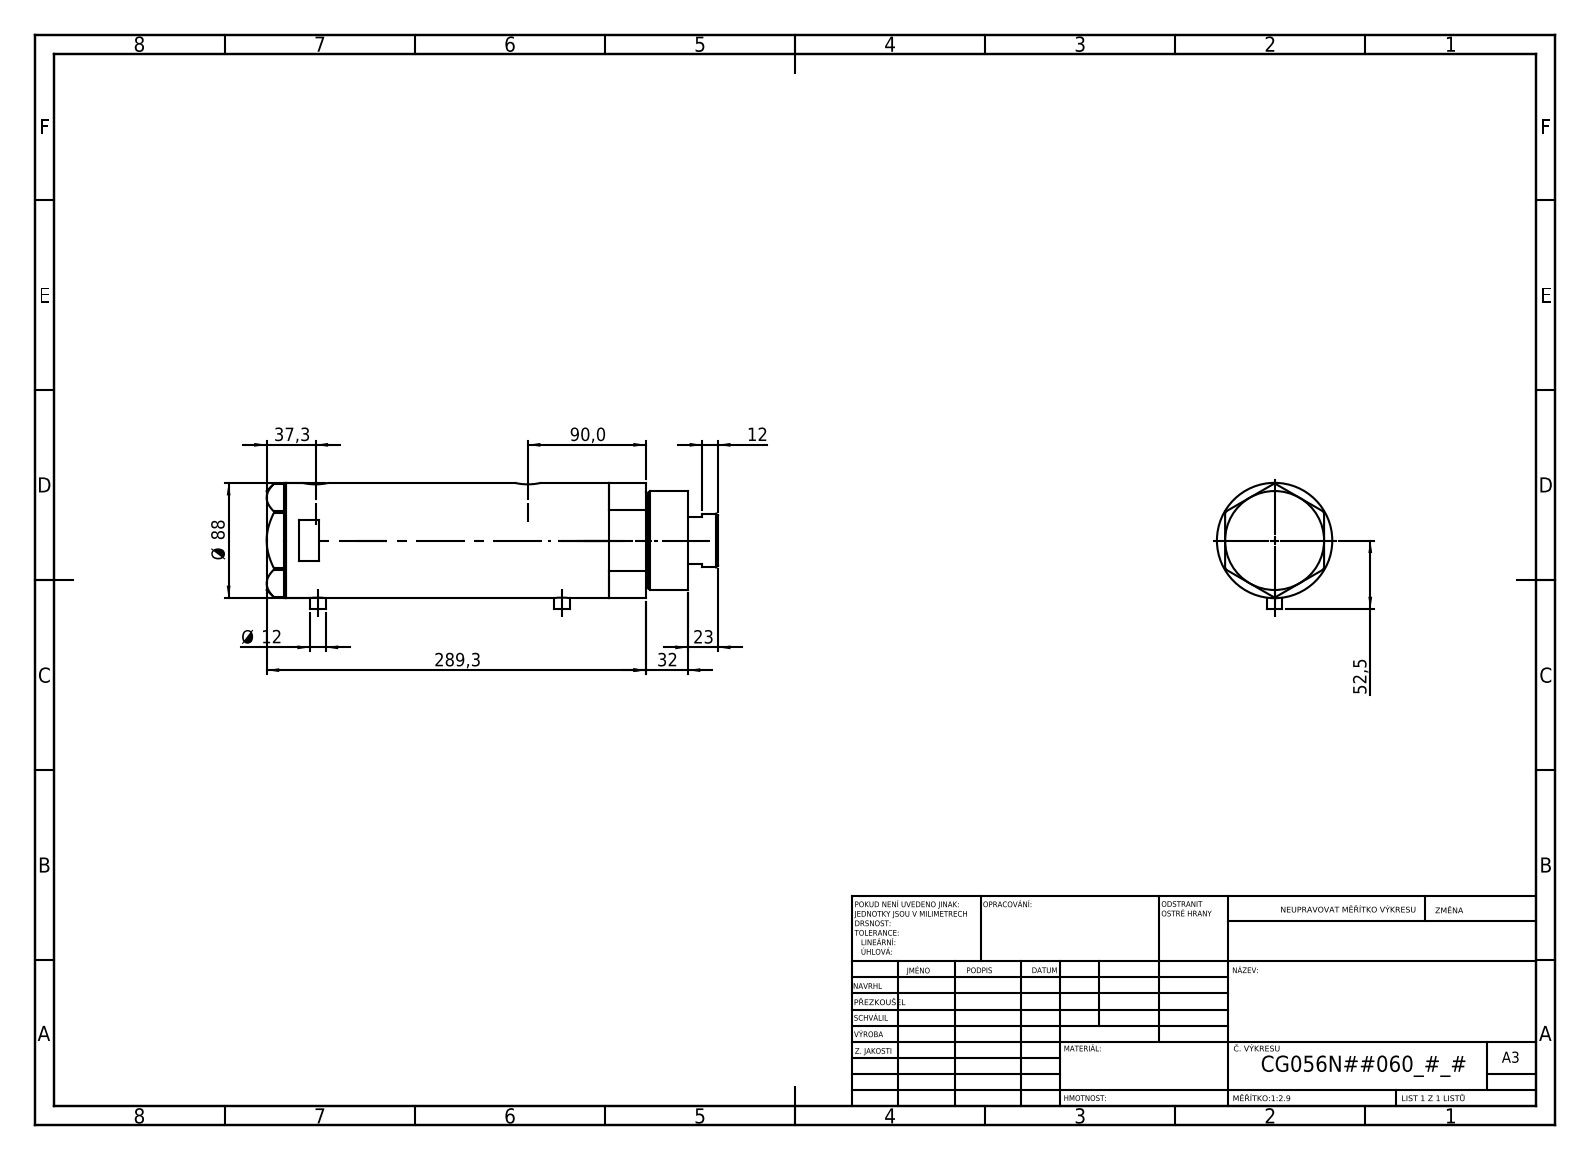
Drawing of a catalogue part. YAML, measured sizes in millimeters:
part_name: "V270CG_FRONT; V270CG_VC; V270CG_BACK; V270CG_MIDDLE"
step_written_by: "SolidWorks 2019 (CONFIG_CONTROL_DESIGN)"
units: millimeters
bodies: {solids: 4, faces: 121, planar: 52, cylindrical: 49, other: 20}
overall_size: [344.3, 96.5, 88]
volume: 1827000
surface_area: 252410
round_holes:
  - {diameter: 12.5, count: 2}
  - {diameter: 13.16, count: 2}
  - {diameter: 20, count: 2}
  - {diameter: 14.5, count: 1}
  - {diameter: 42, count: 1}
  - {diameter: 43.5, count: 1}
  - {diameter: 56, count: 1}
  - {diameter: 60, count: 1}
  - {diameter: 80, count: 1}
round_bosses_or_shafts:
  - {diameter: 12, count: 2}
  - {diameter: 88, count: 1}
  - {diameter: 75, count: 1}
  - {diameter: 73, count: 1}
  - {diameter: 41, count: 1}
face_to_face_distances: [184.4, 26, 158.4, 15, 41, 199.4, 306.3, 321.3, 280.3, 121.9]
hole_center_spacings: [1.7, 25.8, 160.3, 162, 186.1, 187.8]
